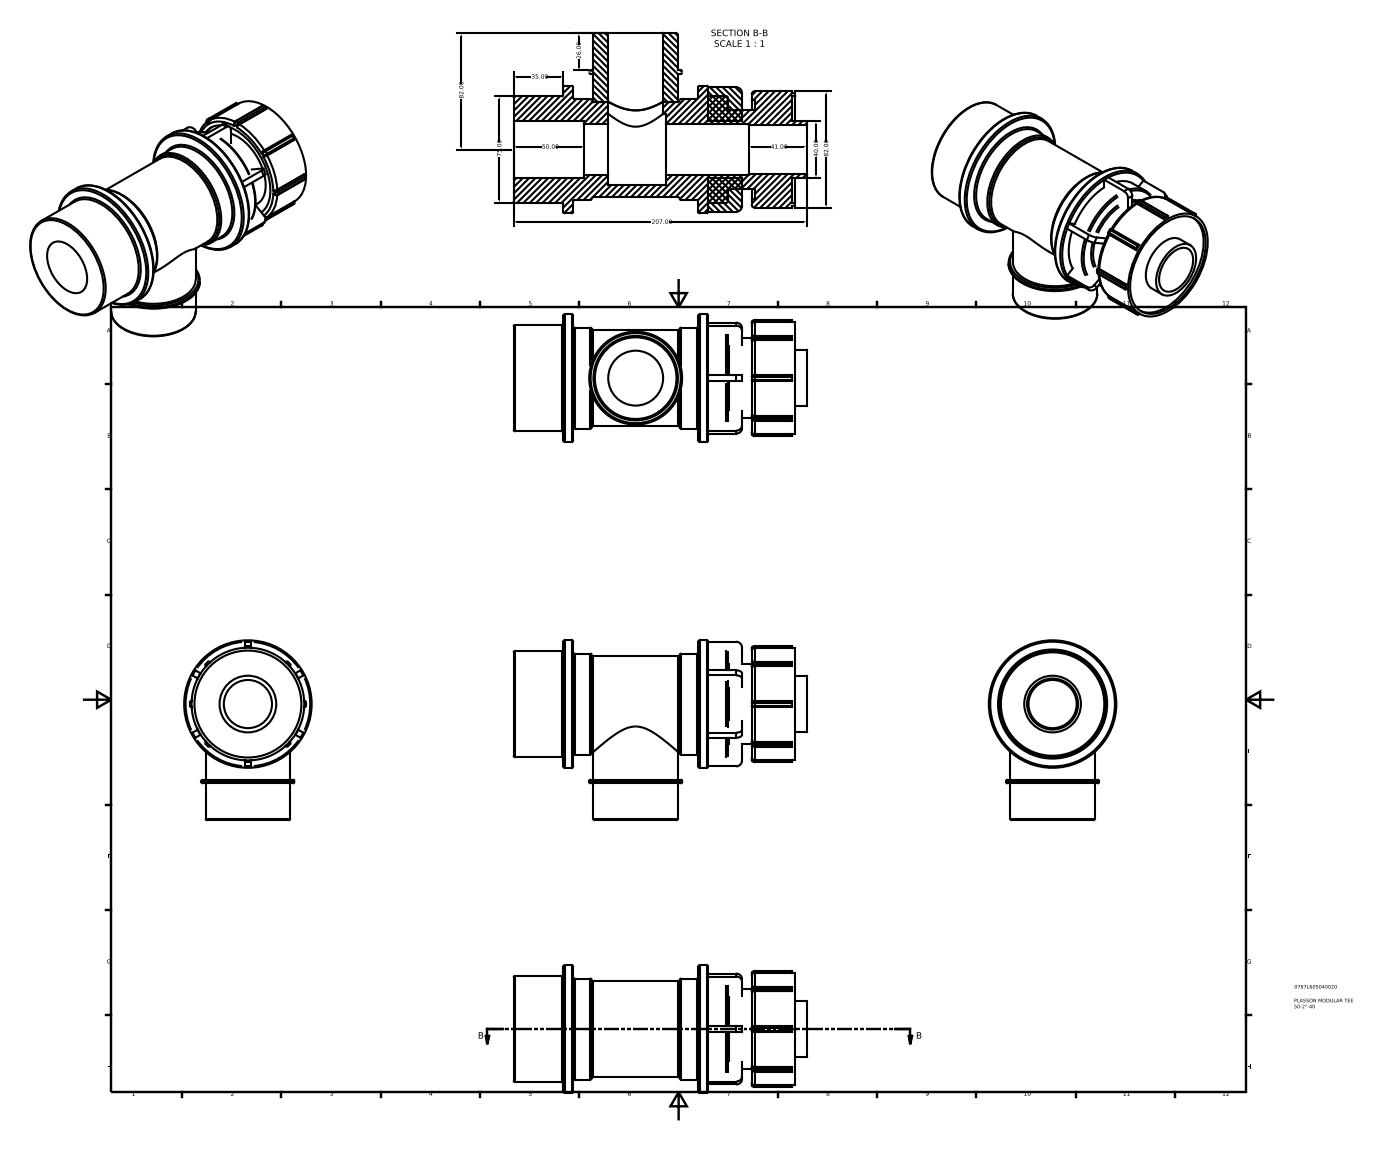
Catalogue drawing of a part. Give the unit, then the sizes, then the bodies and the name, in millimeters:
Units: millimetres
Overall size (bounding box): 207 × 127 × 90
Round holes (diameter × count): ⌀34 ×1, ⌀36 ×1, ⌀38.75 ×1, ⌀40 ×1, ⌀50.4 ×1, ⌀67.5 ×1, ⌀69.7 ×1, ⌀75.44 ×1
Round bosses / shafts (diameter × count): ⌀90 ×1, ⌀79.54 ×1, ⌀75 ×1, ⌀71.25 ×1, ⌀65.58 ×1, ⌀59.61 ×1, ⌀56.25 ×1
Partial cylindrical surfaces — rounded edges, fillets, slot ends (radius × count): R1 ×28, R2 ×8, R4.1 ×6
Main face-to-face distances: 4.1, 95.3, 7, 196.75, 137.3, 59.45, 42, 154.75, 130.3, 88.3
Volume: 660 746 mm³ · Surface area: 124 780 mm²
Bodies: 8 solids, 212 faces (86 planar, 69 cylindrical, 57 other)
Part name (STEP PRODUCT): 0787L605040020
STEP written by: Autodesk Inventor 2015 (AUTOMOTIVE_DESIGN)
